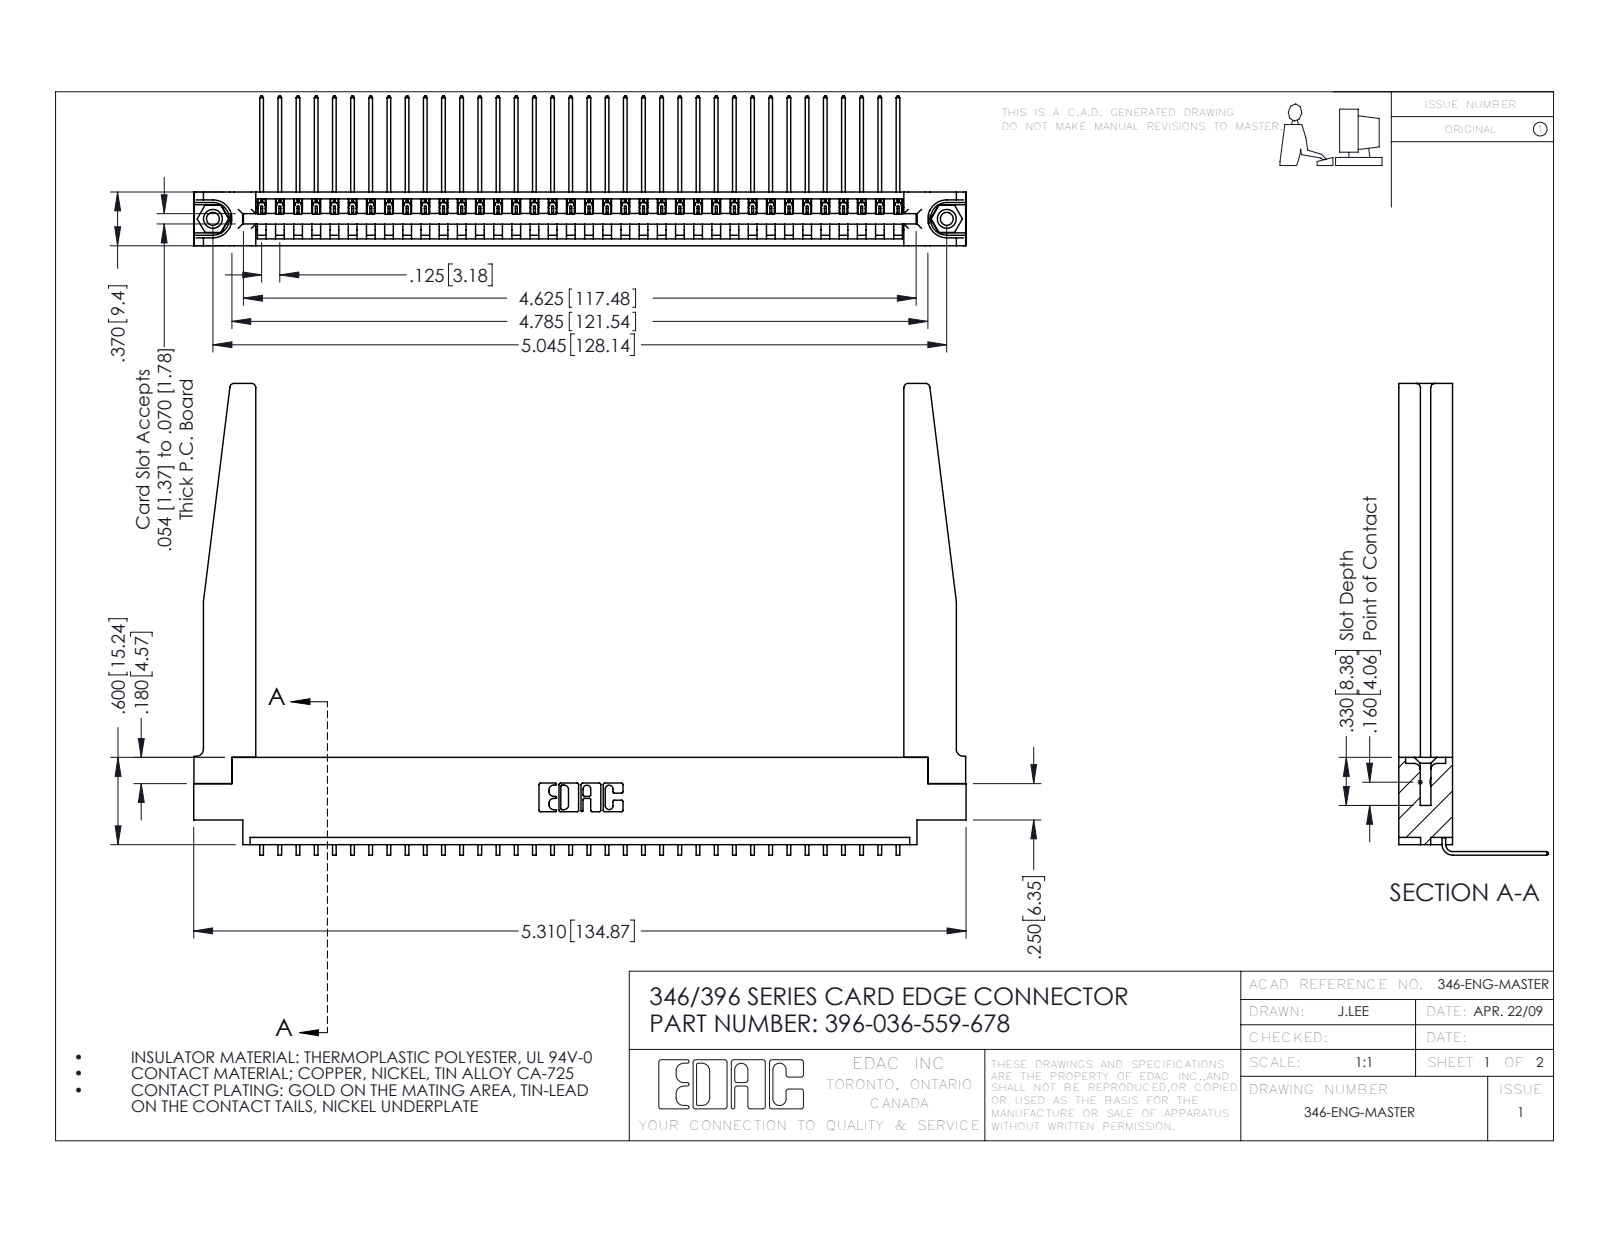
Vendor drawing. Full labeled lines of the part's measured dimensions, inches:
Part name (STEP PRODUCT): 346-220-078_345-220-078; 345-292-001_558 559 Tail - 1; 346 Part_0.170 Offset - 0.156 Dia-TH; 396-036-559-678 (+1 more)
STEP written by: SolidWorks 2016 (CONFIG_CONTROL_DESIGN)
Units: inches
Bodies: 41 solids, 2520 faces (1734 planar, 734 cylindrical, 52 other)
Overall size (bounding box): 5.31 × 3.243 × 1.03
Volume: 1.205 in³ · Surface area: 36.26 in²
Round holes (diameter × count): ⌀0.089 ×2, ⌀0.125 ×2, ⌀0.156 ×2, ⌀0.064 ×1
Round bosses / shafts (diameter × count): ⌀0.155 ×2
Partial cylindrical surfaces — rounded edges, fillets, slot ends (radius × count): R0.006 ×72, R0.01 ×22, R0.03 ×8, R0.007 ×6, R0.031 ×6, R0.026 ×3, R0.05 ×3, R0.031 ×2
Main face-to-face distances: 0.37, 0.048, 0.322, 0.072, 0.148, 0.15, 0.025, 0.25, 0.298, 0.222
Hole centre spacings: 0.246, 4.836, 5.045
